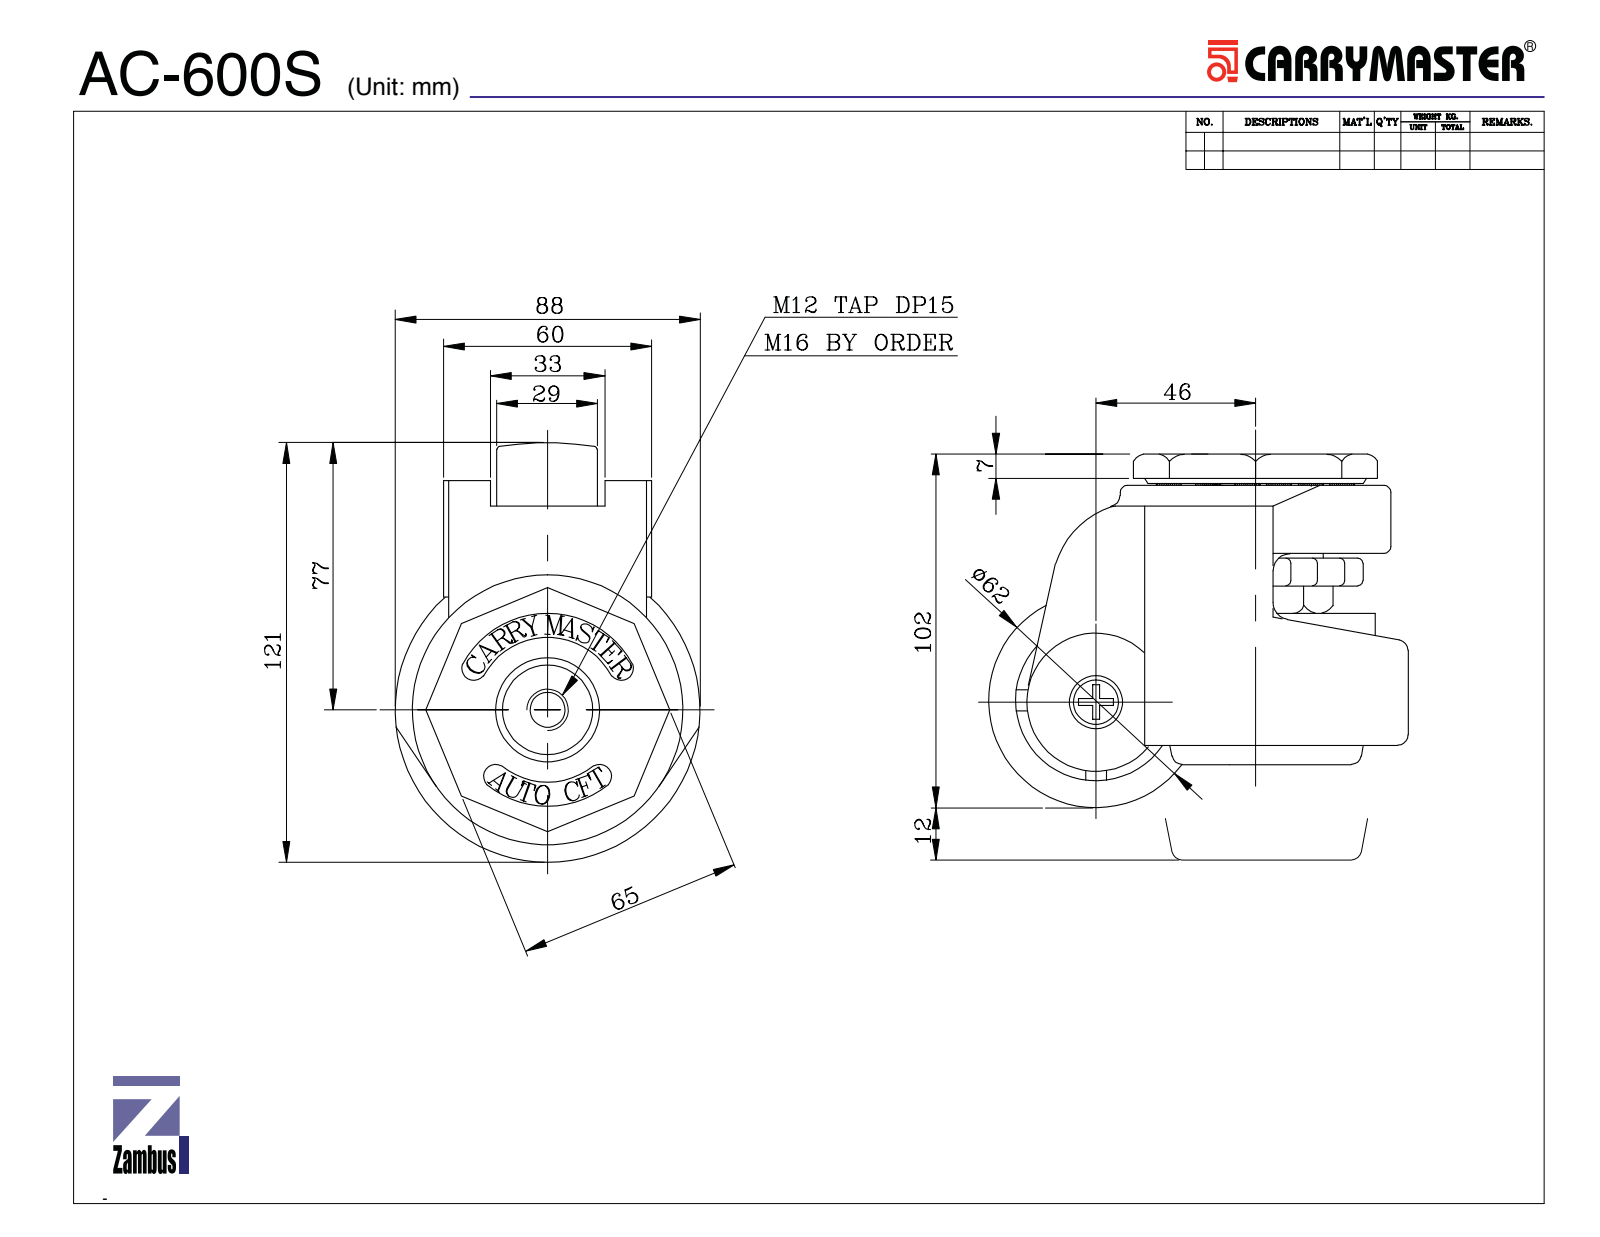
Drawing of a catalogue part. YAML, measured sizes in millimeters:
part_name: "AC-600S"
step_written_by: "SolidWorks 2015 (CONFIG_CONTROL_DESIGN)"
units: millimeters
bodies: {solids: 44, faces: 1829, planar: 786, cylindrical: 371, other: 672}
overall_size: [119.5, 103.2, 87]
volume: 407059
surface_area: 129139
round_holes:
  - {diameter: 2.5, count: 1}
  - {diameter: 3.68, count: 1}
  - {diameter: 6.8, count: 1}
  - {diameter: 8.7, count: 1}
  - {diameter: 10.1, count: 1}
  - {diameter: 10.2, count: 1}
  - {diameter: 12.2, count: 1}
  - {diameter: 13, count: 1}
  - {diameter: 14.5, count: 1}
  - {diameter: 17.5, count: 1}
  - {diameter: 21.5, count: 1}
  - {diameter: 29.1, count: 1}
round_bosses_or_shafts:
  - {diameter: 24, count: 2}
  - {diameter: 12, count: 2}
  - {diameter: 41.2, count: 1}
  - {diameter: 38, count: 1}
  - {diameter: 25, count: 1}
  - {diameter: 22, count: 1}
  - {diameter: 20, count: 1}
  - {diameter: 16.5, count: 1}
partial_cylinders:
  - {radius: 1.5, count: 48}
  - {radius: 2, count: 18}
  - {radius: 1, count: 13}
  - {radius: 7.2, count: 8}
  - {radius: 3, count: 6}
  - {radius: 4, count: 4}
  - {radius: 4.5, count: 2}
  - {radius: 4.51, count: 2}
face_to_face_distances: [10, 43, 1.5, 29, 33, 16.7, 30.76, 4, 55.96, 10.75]
